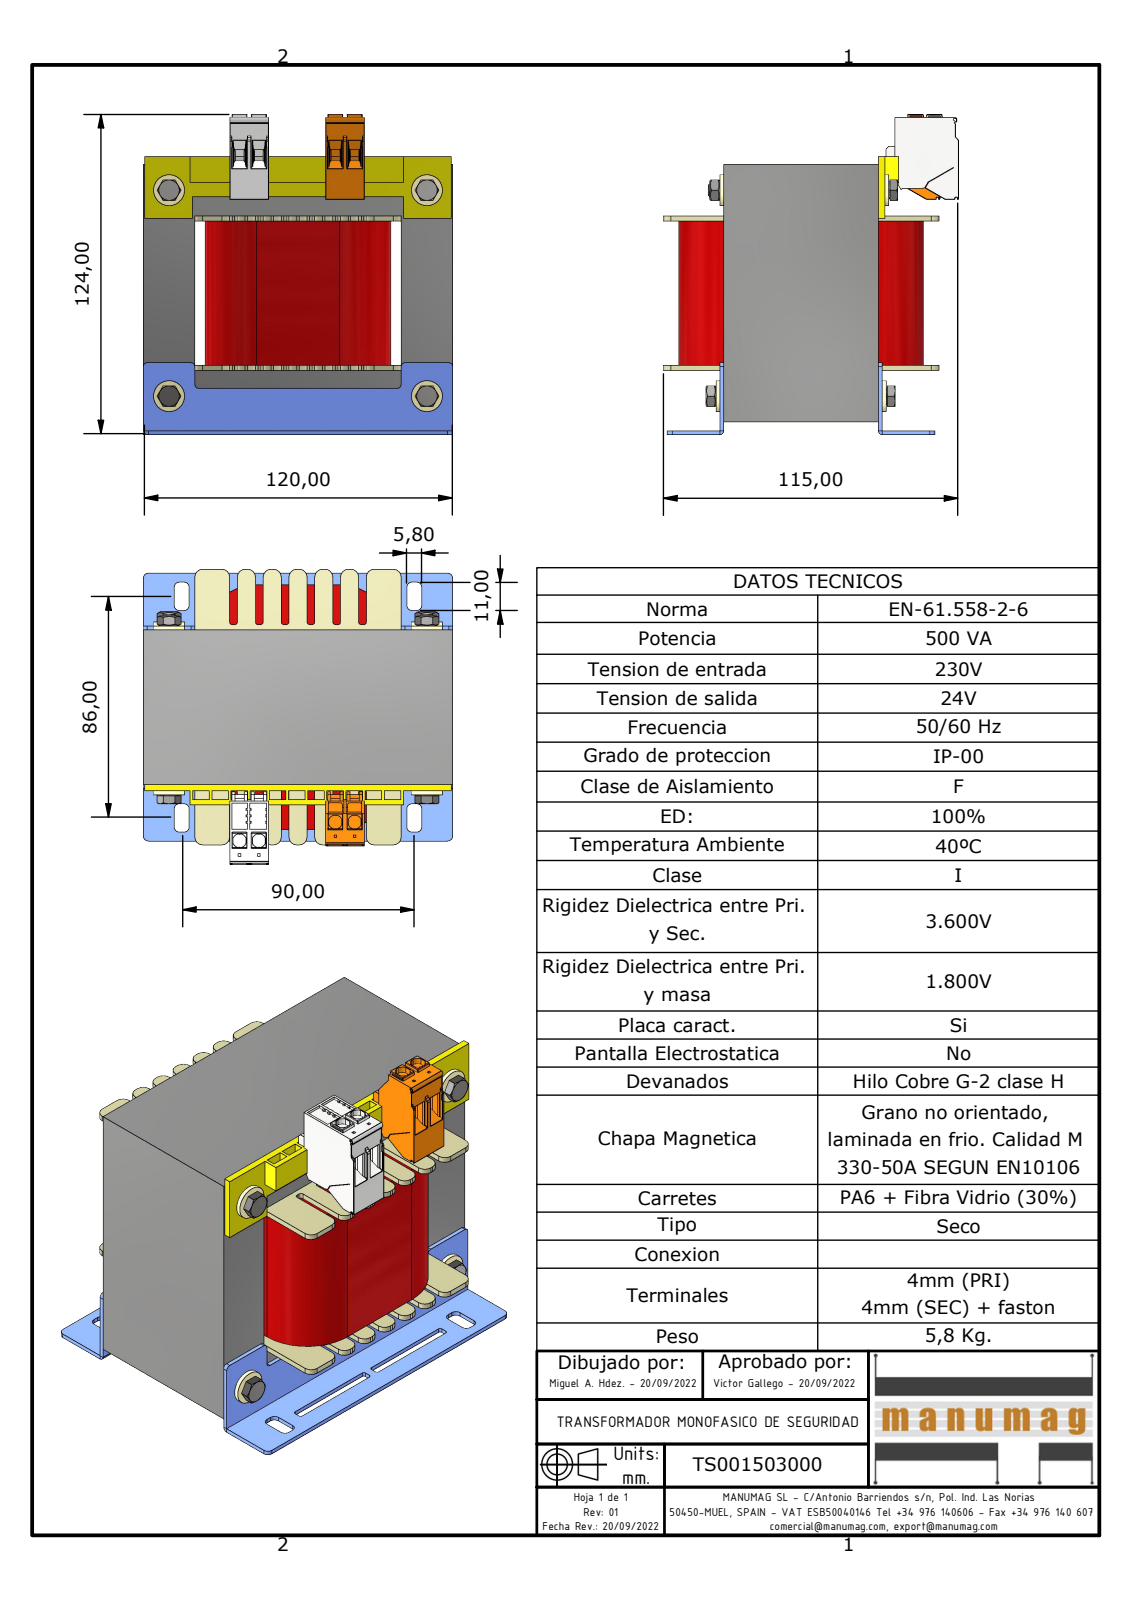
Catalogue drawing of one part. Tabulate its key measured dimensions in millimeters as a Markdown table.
| quantity | value |
| --- | --- |
| part name | TS001503000; EI120 x 100 - 60 (Rc40); AF40DIN; EI120 (+6 more) |
| STEP written by | Autodesk Inventor 2023 (AUTOMOTIVE_DESIGN) |
| units | millimeters |
| bodies | 23 solids, 3908 faces (3099 planar, 566 cylindrical, 243 other) |
| overall size | 124.5 × 120 × 114.65 |
| volume | 860 592 mm³ |
| surface area | 166 238 mm² |
| round holes (diameter × count) | 4.13 × 4, 5 × 4, 6.6 × 4, 6.8 × 2 |
| round bosses / shafts (diameter × count) | 12 × 4, 6.7 × 4, 5.9 × 4, 4.57 × 4 |
| partial cylindrical surfaces (radius × count) | 0.15 × 163, 0.2 × 58, 1 × 32, 3 × 28, 2 × 20, 0.8 × 18, 0.5 × 14, 0.3 × 12 |
| main face-to-face distances | 80, 20, 60, 40, 100, 1.5, 16, 56, 4, 24 |
| hole center spacings | 80, 100, 128.06 |
